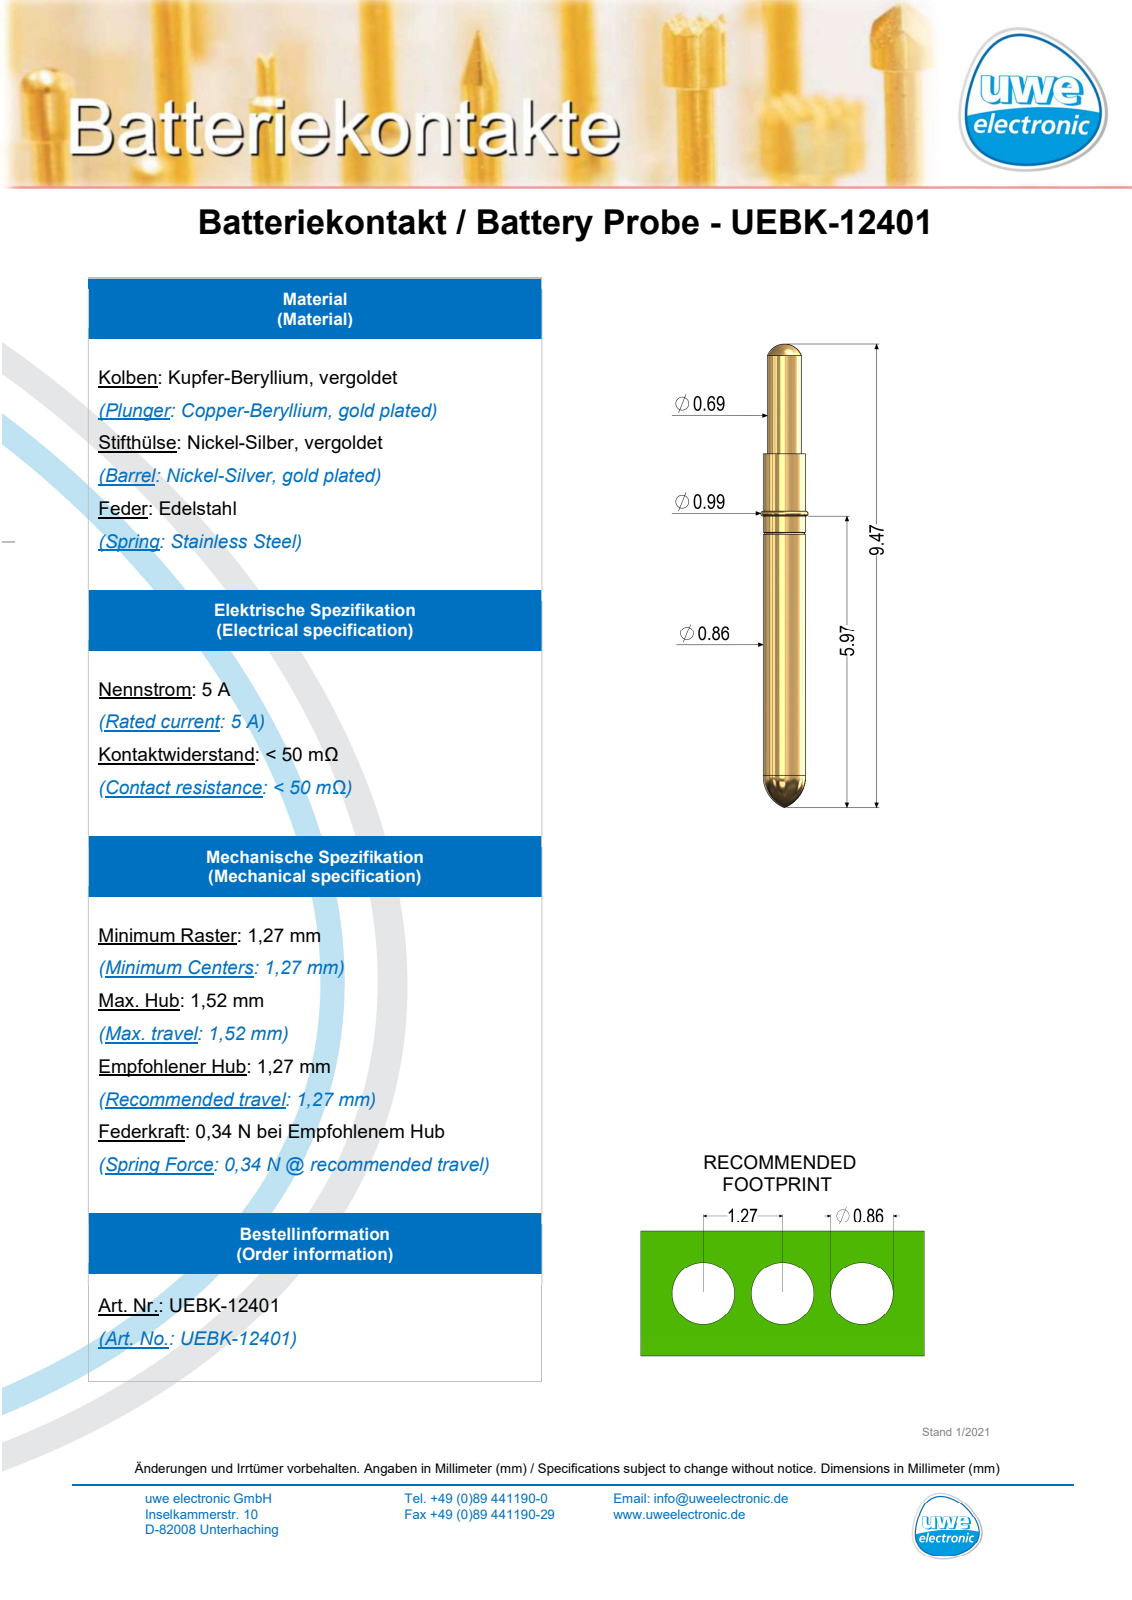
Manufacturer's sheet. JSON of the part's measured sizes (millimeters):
{"part_name": "UEBK-12401", "step_written_by": "SolidWorks 2017 (AUTOMOTIVE_DESIGN)", "units": "millimeters", "bodies": {"solids": 1, "faces": 19, "planar": 1, "cylindrical": 8, "other": 10}, "overall_size": [9.47, 0.96, 0.96], "volume_mm3": 5, "surface_area_mm2": 25, "round_bosses_or_shafts": [[0.86, 1], [0.69, 1]]}
